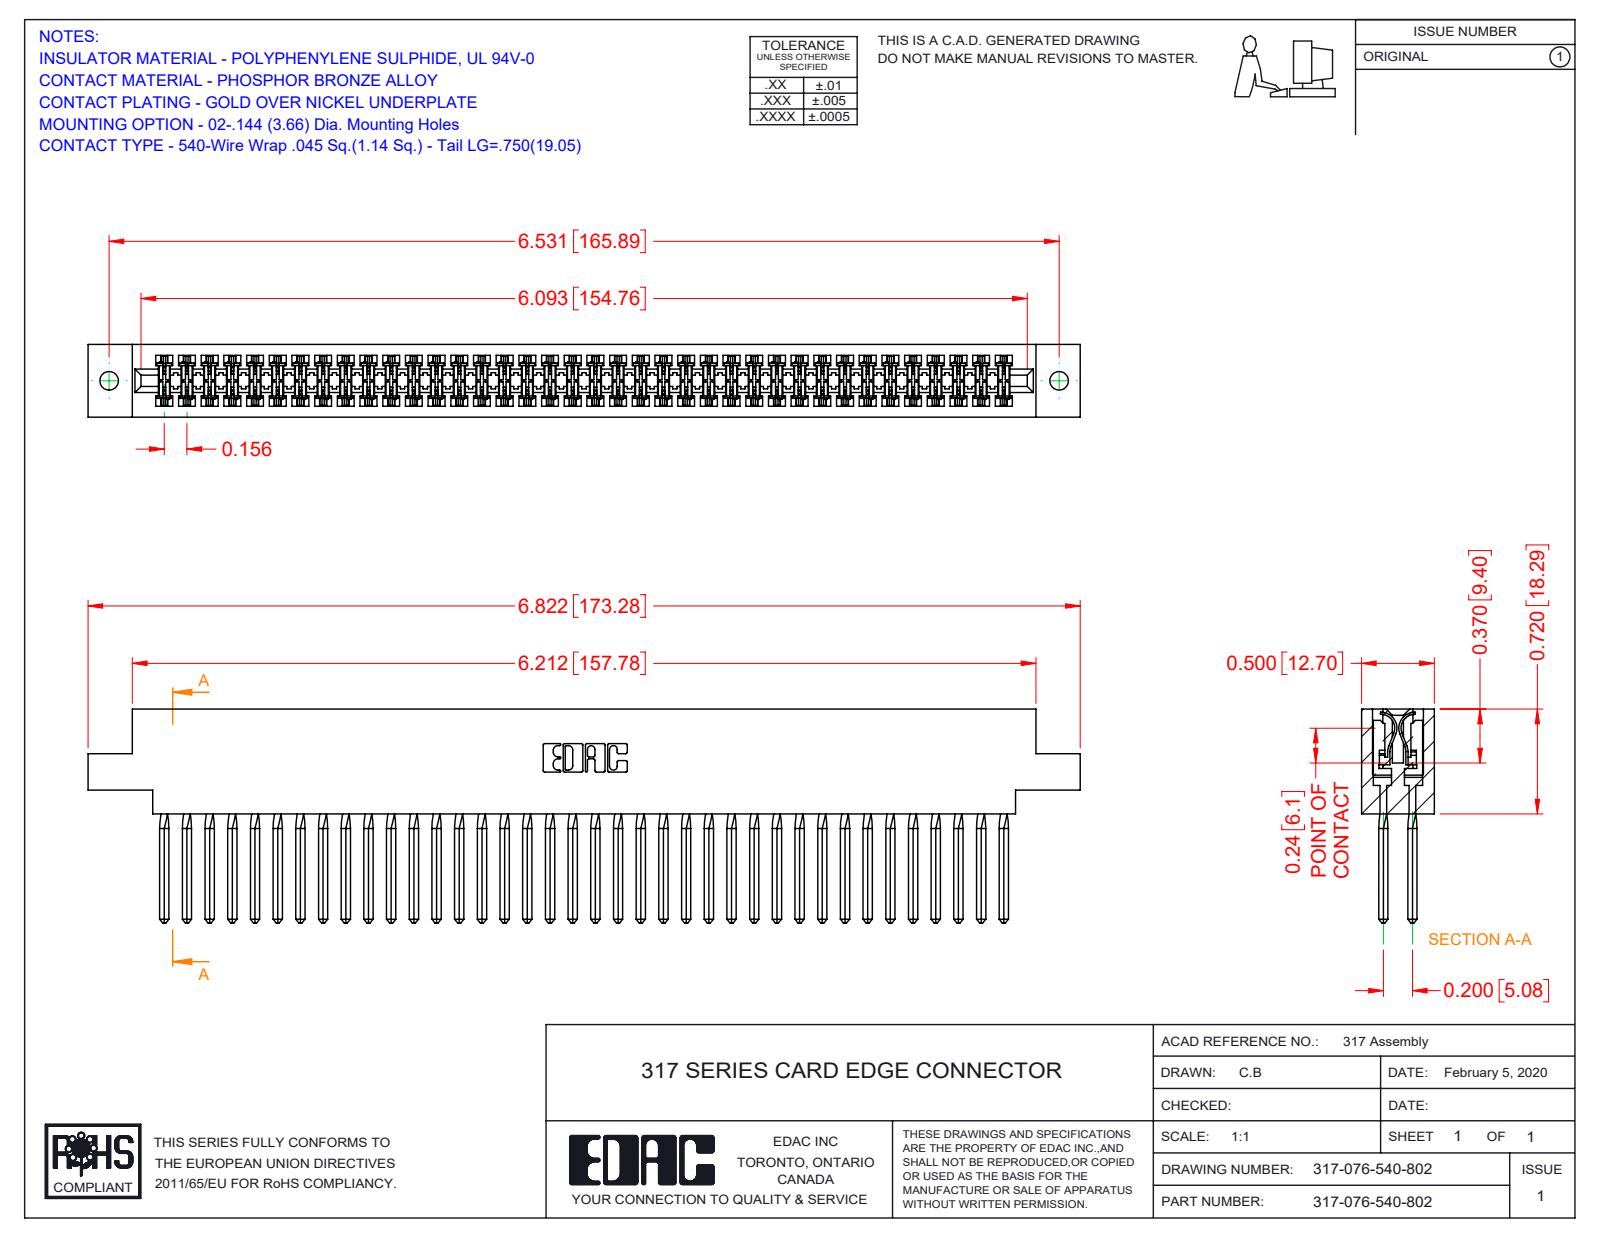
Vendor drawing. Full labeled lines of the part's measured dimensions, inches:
Part name (STEP PRODUCT): 317 Part_.144 Dia; 317-076-540-802; 317-290-001_540
STEP written by: SolidWorks 2016 (CONFIG_CONTROL_DESIGN)
Units: inches
Bodies: 77 solids, 6866 faces (5606 planar, 956 cylindrical, 304 other)
Overall size (bounding box): 6.822 × 1.47 × 0.5
Volume: 1.764 in³ · Surface area: 66.17 in²
Round holes (diameter × count): ⌀0.128 ×2
Partial cylindrical surfaces — rounded edges, fillets, slot ends (radius × count): R0.015 ×152, R0.01 ×22, R0.007 ×6, R0.031 ×6, R0.026 ×3, R0.095 ×2, R0.1 ×2, R0.11 ×2
Main face-to-face distances: 0.5, 0.075, 0.425, 0.35, 0.195, 0.094, 0.11, 0.2, 0.115, 0.131
Hole centre spacings: 6.531
